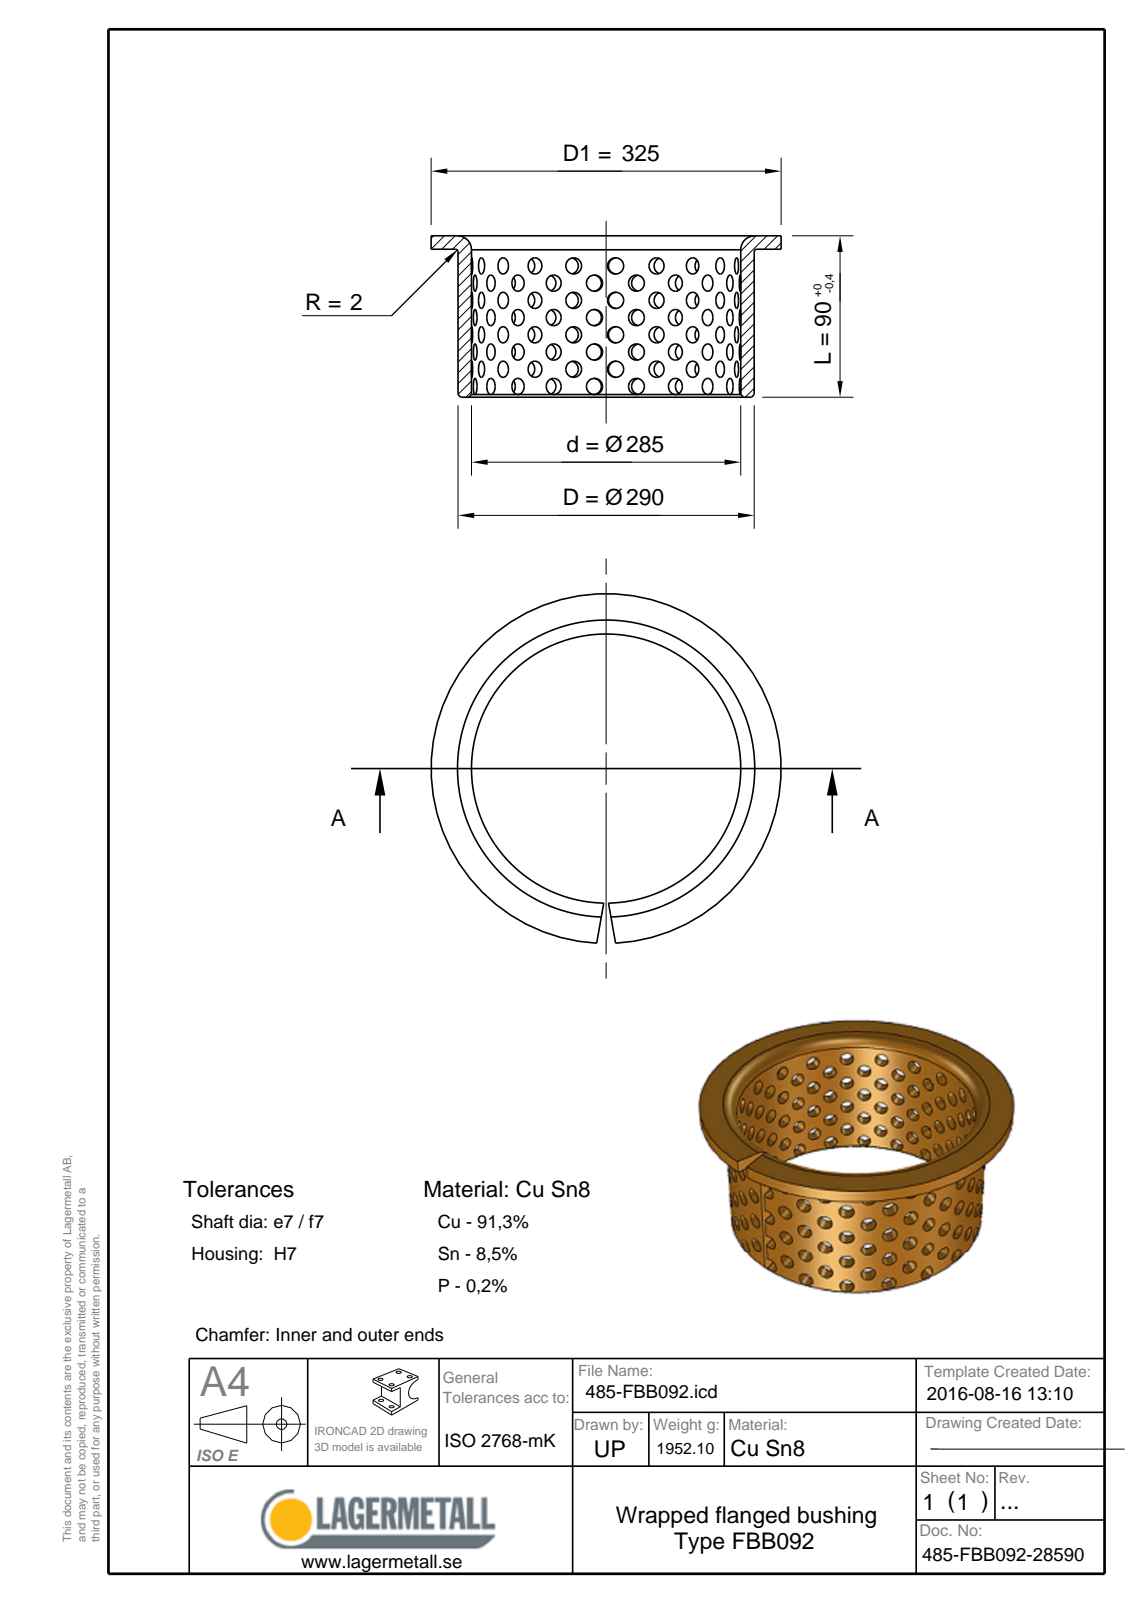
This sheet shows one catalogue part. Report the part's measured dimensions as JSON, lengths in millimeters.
{"part_name": "485-FBB092-28590", "step_written_by": "Spatial InterOp 3D (CONFIG_CONTROL_DESIGN)", "units": "millimeters", "bodies": {"solids": 1, "faces": 12, "planar": 5, "cylindrical": 3, "other": 4}, "overall_size": [325, 324.95, 90], "volume_mm3": 241000, "surface_area_mm2": 197878, "round_holes": [[285, 1]], "round_bosses_or_shafts": [[325, 1], [290, 1]], "face_to_face_distances": [2.5, 87.5, 90]}
